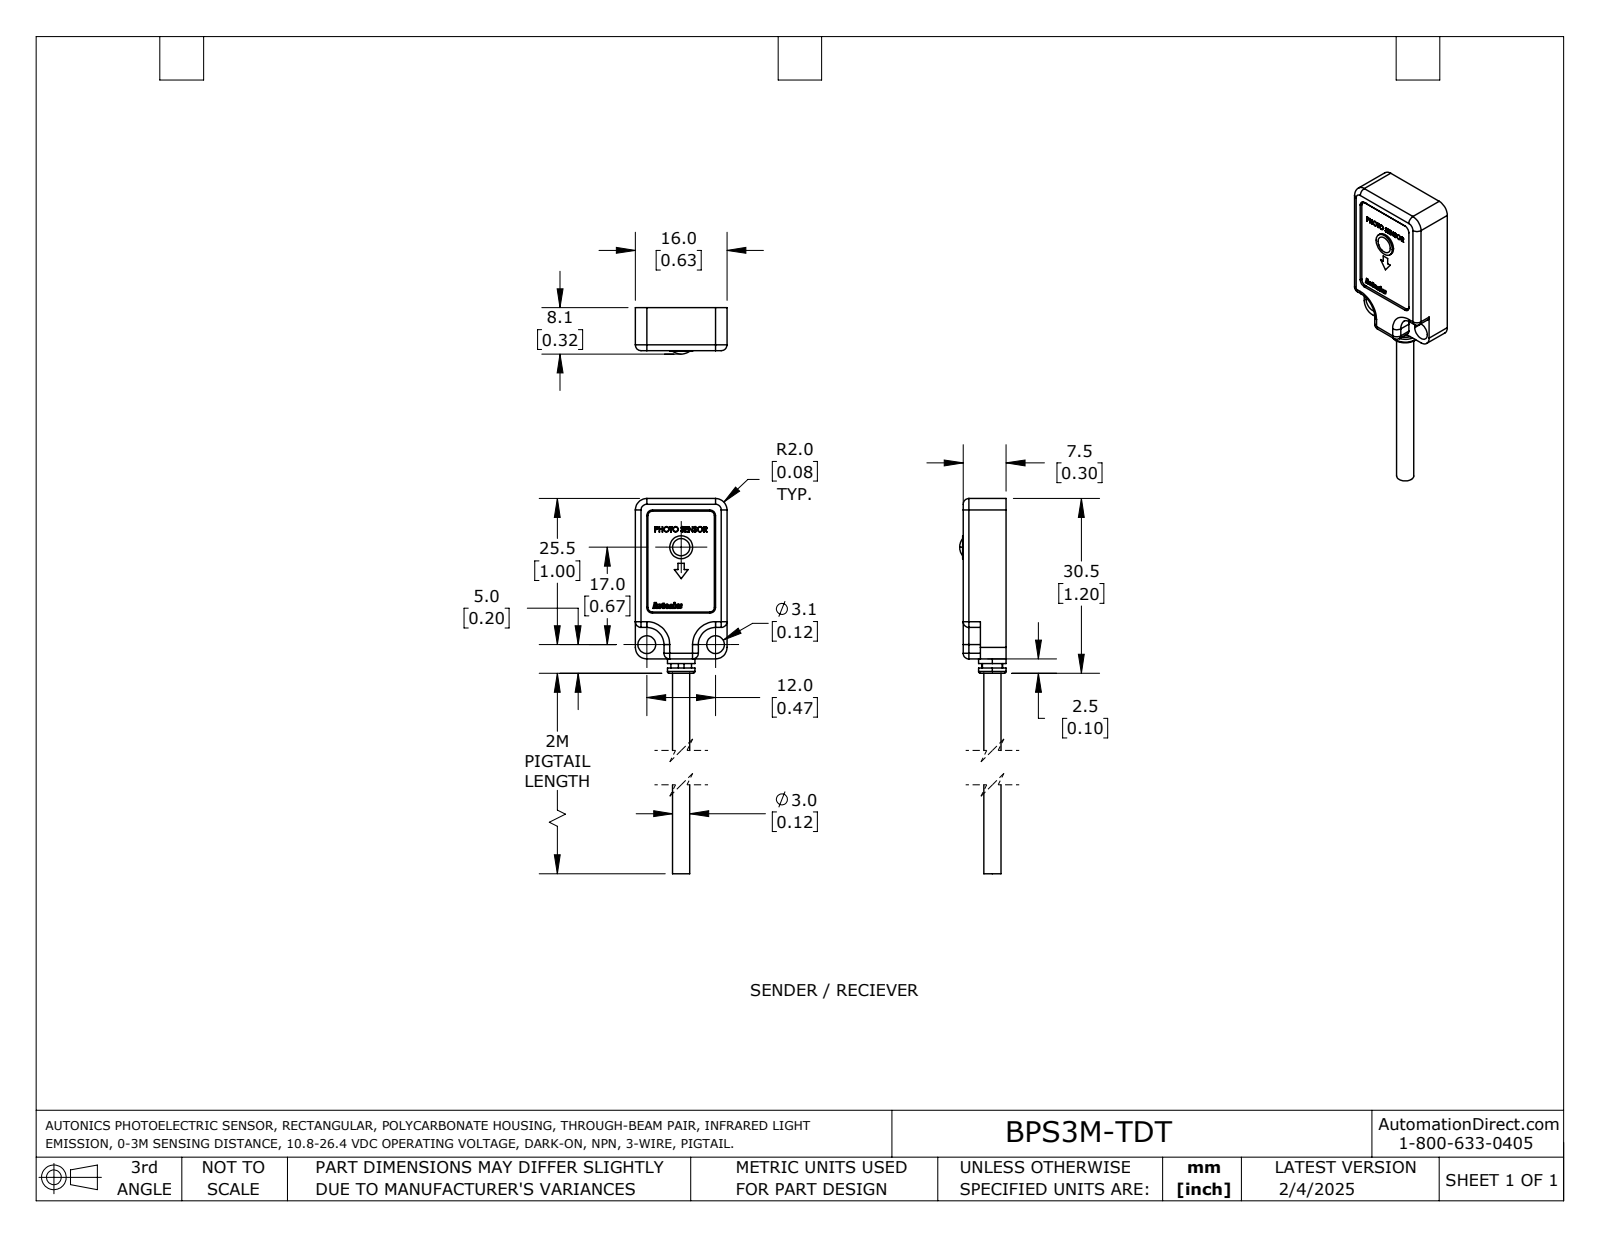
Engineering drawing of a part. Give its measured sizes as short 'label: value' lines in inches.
name: BPS3M-TDT_BPS3M-TDT-P_BPS3M-TDTL_BPS3M-TDTL-P; RIGHT; LEFT
written by: SolidWorks 2024 (AUTOMOTIVE_DESIGN)
unit: in
bodies: 2 solids, 226 faces (116 planar, 86 cylindrical, 24 other)
size: 3.575 × 2.382 × 0.63
volume: 0.404 in³; area: 5.951 in²
holes: 2× ⌀0.122
bosses: 2× ⌀0.189, 2× ⌀0.142, 2× ⌀0.118, 1× ⌀0.157
rounds: 22× R0.039, 4× R0.031, 4× R0.079, 2× R0.118
face distances: 3.575, 0.287, 3.287, 0.63, 3, 0.295, 3.28, 2.992, 2.984, 1.102
hole spacings: 0.472
